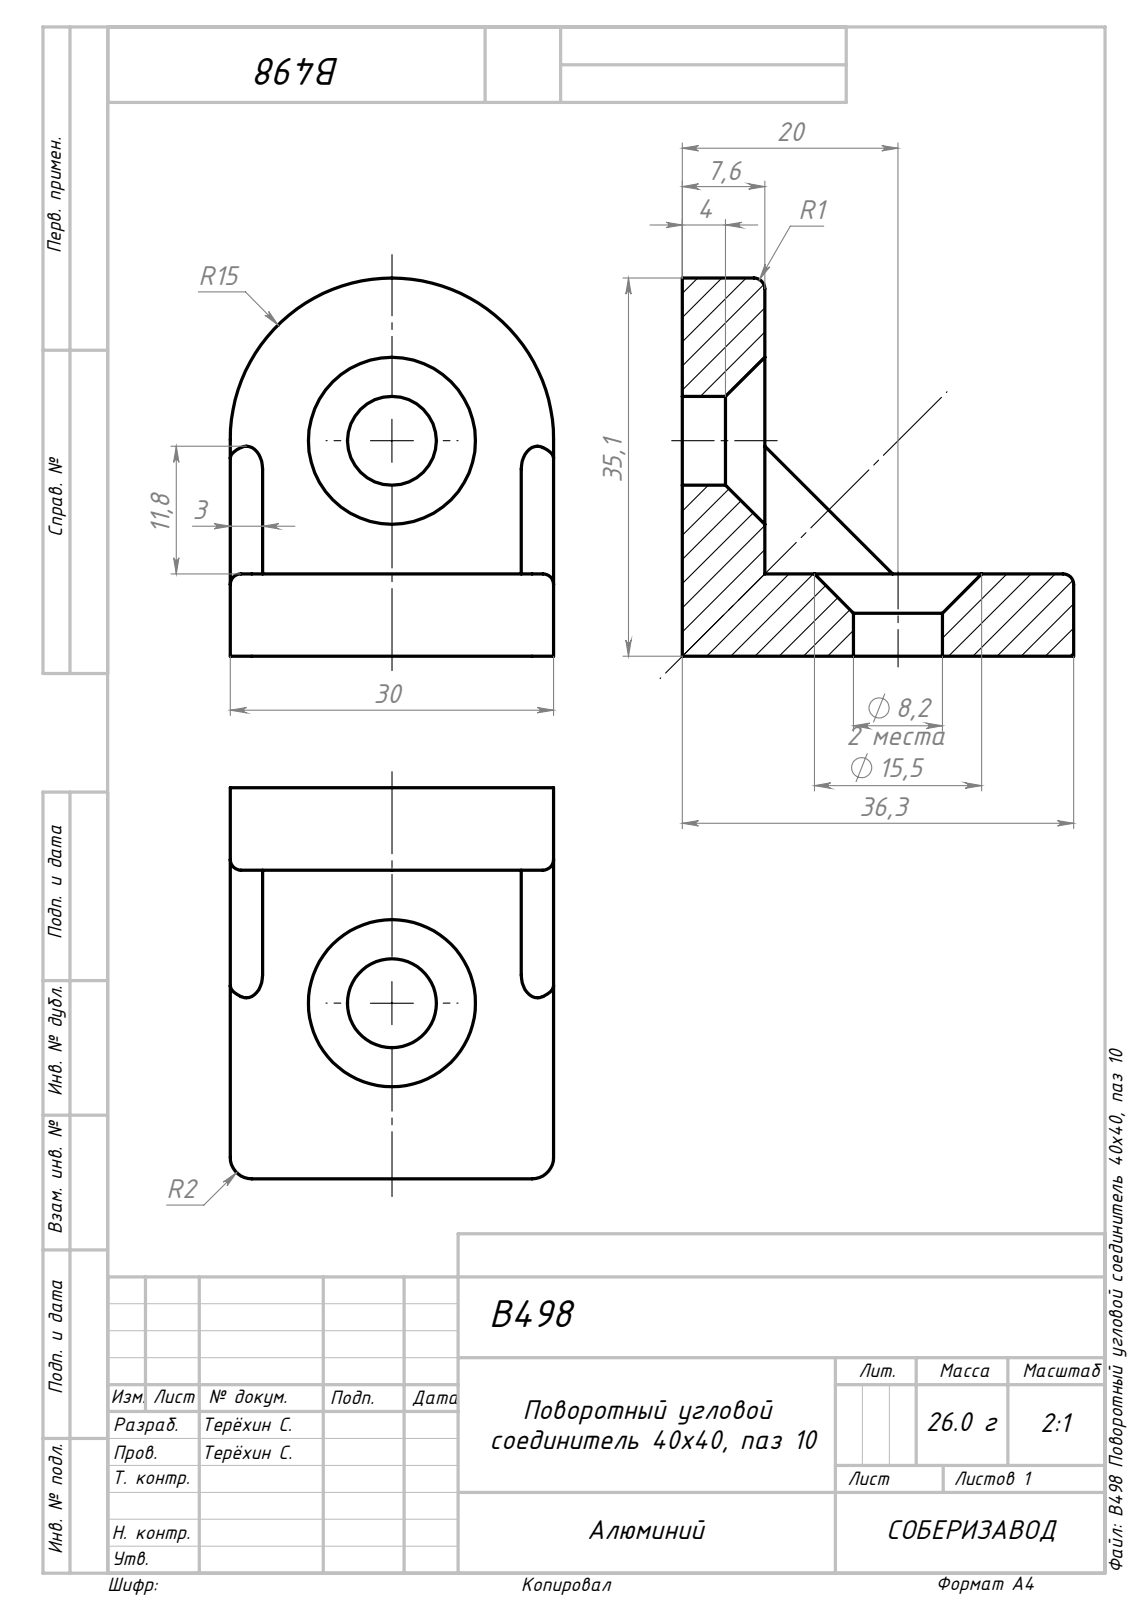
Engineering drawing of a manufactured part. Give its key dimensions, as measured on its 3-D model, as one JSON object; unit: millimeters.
{"part_name": "B498 Поворотный угловой соединитель 40x40, паз 10", "step_written_by": "SolidWorks 2022 (AUTOMOTIVE_DESIGN)", "units": "millimeters", "bodies": {"solids": 1, "faces": 34, "planar": 9, "cylindrical": 17, "other": 8}, "overall_size": [36.3, 35.1, 30], "volume_mm3": 12984, "surface_area_mm2": 5209, "round_holes": [[8.25, 2]], "partial_cylinders_radius": [[1, 5], [1.5, 4], [2, 2], [15, 1]], "face_to_face_distances": [7.65, 30, 28.65, 36.3, 3, 27, 24]}
